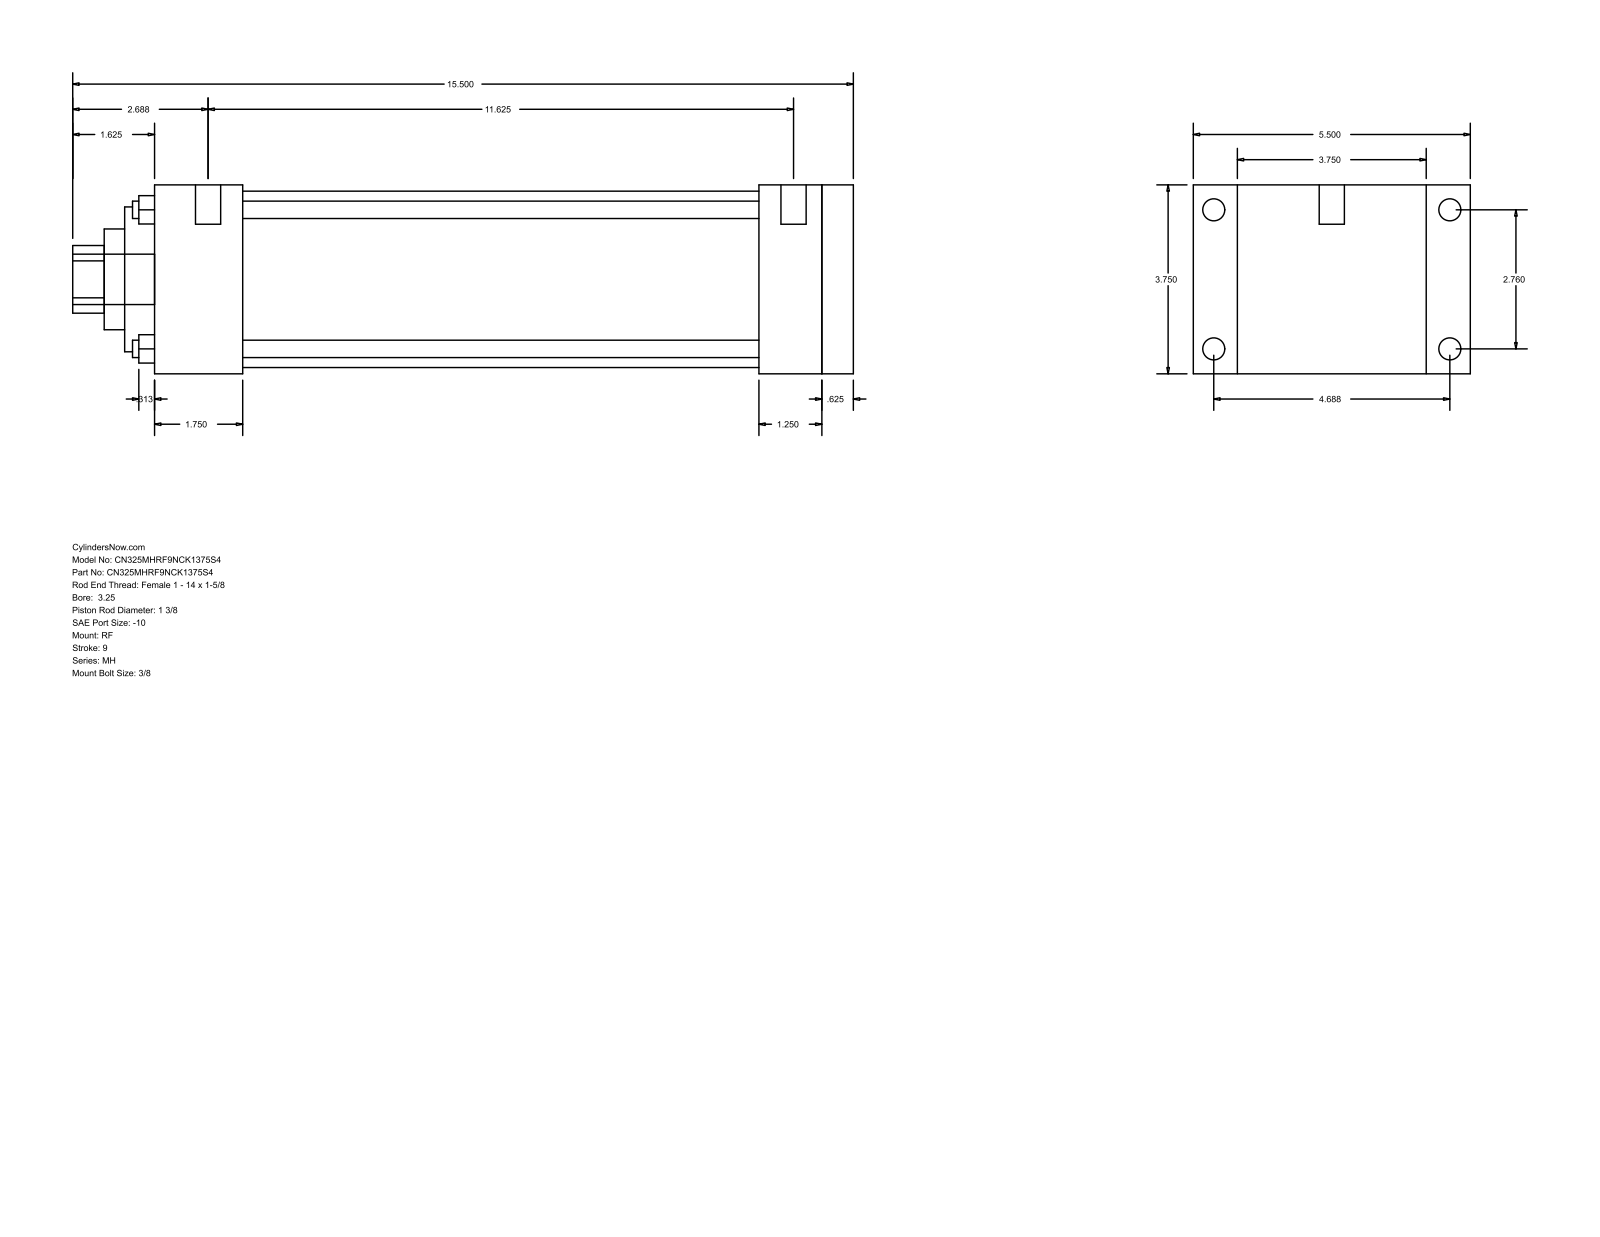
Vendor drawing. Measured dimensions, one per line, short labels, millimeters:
name: MH_RF__0325_1.375
written by: GSSL Pune (CONFIG_CONTROL_DESIGN)
unit: mm
bodies: 0 solids, 94 faces (65 planar, 29 cylindrical, 0 other)
size: 393.7 × 139.7 × 95.25
holes: 4× ⌀8.76, 1× ⌀34.92, 1× ⌀50.8, 1× ⌀73.03, 1× ⌀88.9
bosses: 4× ⌀11.13, 4× ⌀5.56, 2× ⌀12.7, 1× ⌀25.4
rounds: 1× R17.06
face distances: 95.24, 352.43, 15.88, 336.55, 22.23, 117.47, 44.45, 292.1, 307.98, 304.8
hole spacings: 49.57, 70.1, 99.14
